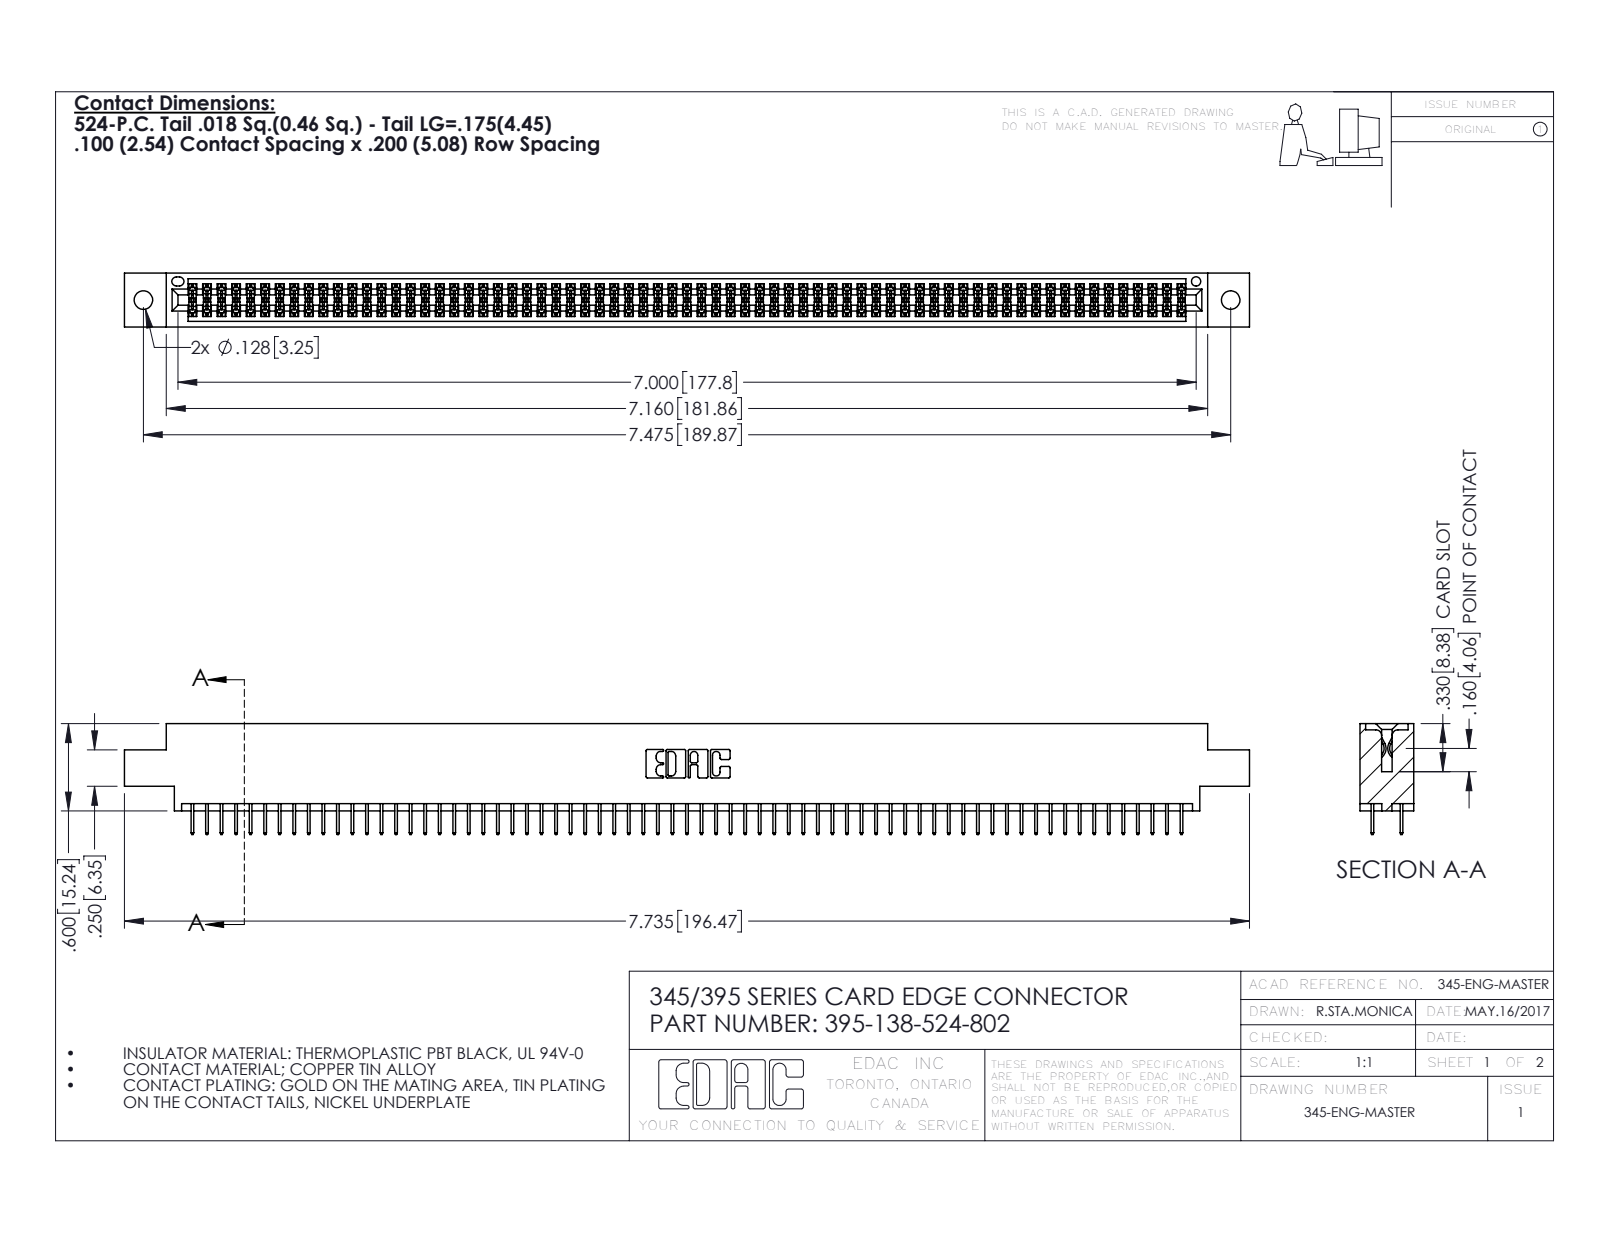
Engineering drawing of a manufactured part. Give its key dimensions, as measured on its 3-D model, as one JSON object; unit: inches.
{"part_name": "395-138-524-802; 345-292-001_345-293-124; 345 Part_0.170 Offset - 0.128 Dia", "step_written_by": "SolidWorks 2016 (CONFIG_CONTROL_DESIGN)", "units": "inches", "bodies": {"solids": 139, "faces": 7582, "planar": 5466, "cylindrical": 2116, "other": 0}, "overall_size": [7.735, 0.762, 0.37], "volume_in3": 1.158, "surface_area_in2": 43.23, "round_holes": [[0.128, 2], [0.064, 1]], "partial_cylinders_radius": [[0.006, 207], [0.01, 22], [0.007, 6], [0.031, 6], [0.026, 3], [0.014, 2], [0.019, 2], [0.022, 2]], "face_to_face_distances": [0.072, 0.298, 0.2, 0.37, 0.098, 0.272, 0.025, 0.225, 0.072, 0.175], "hole_center_spacings": [0.27, 7.239, 7.475]}
